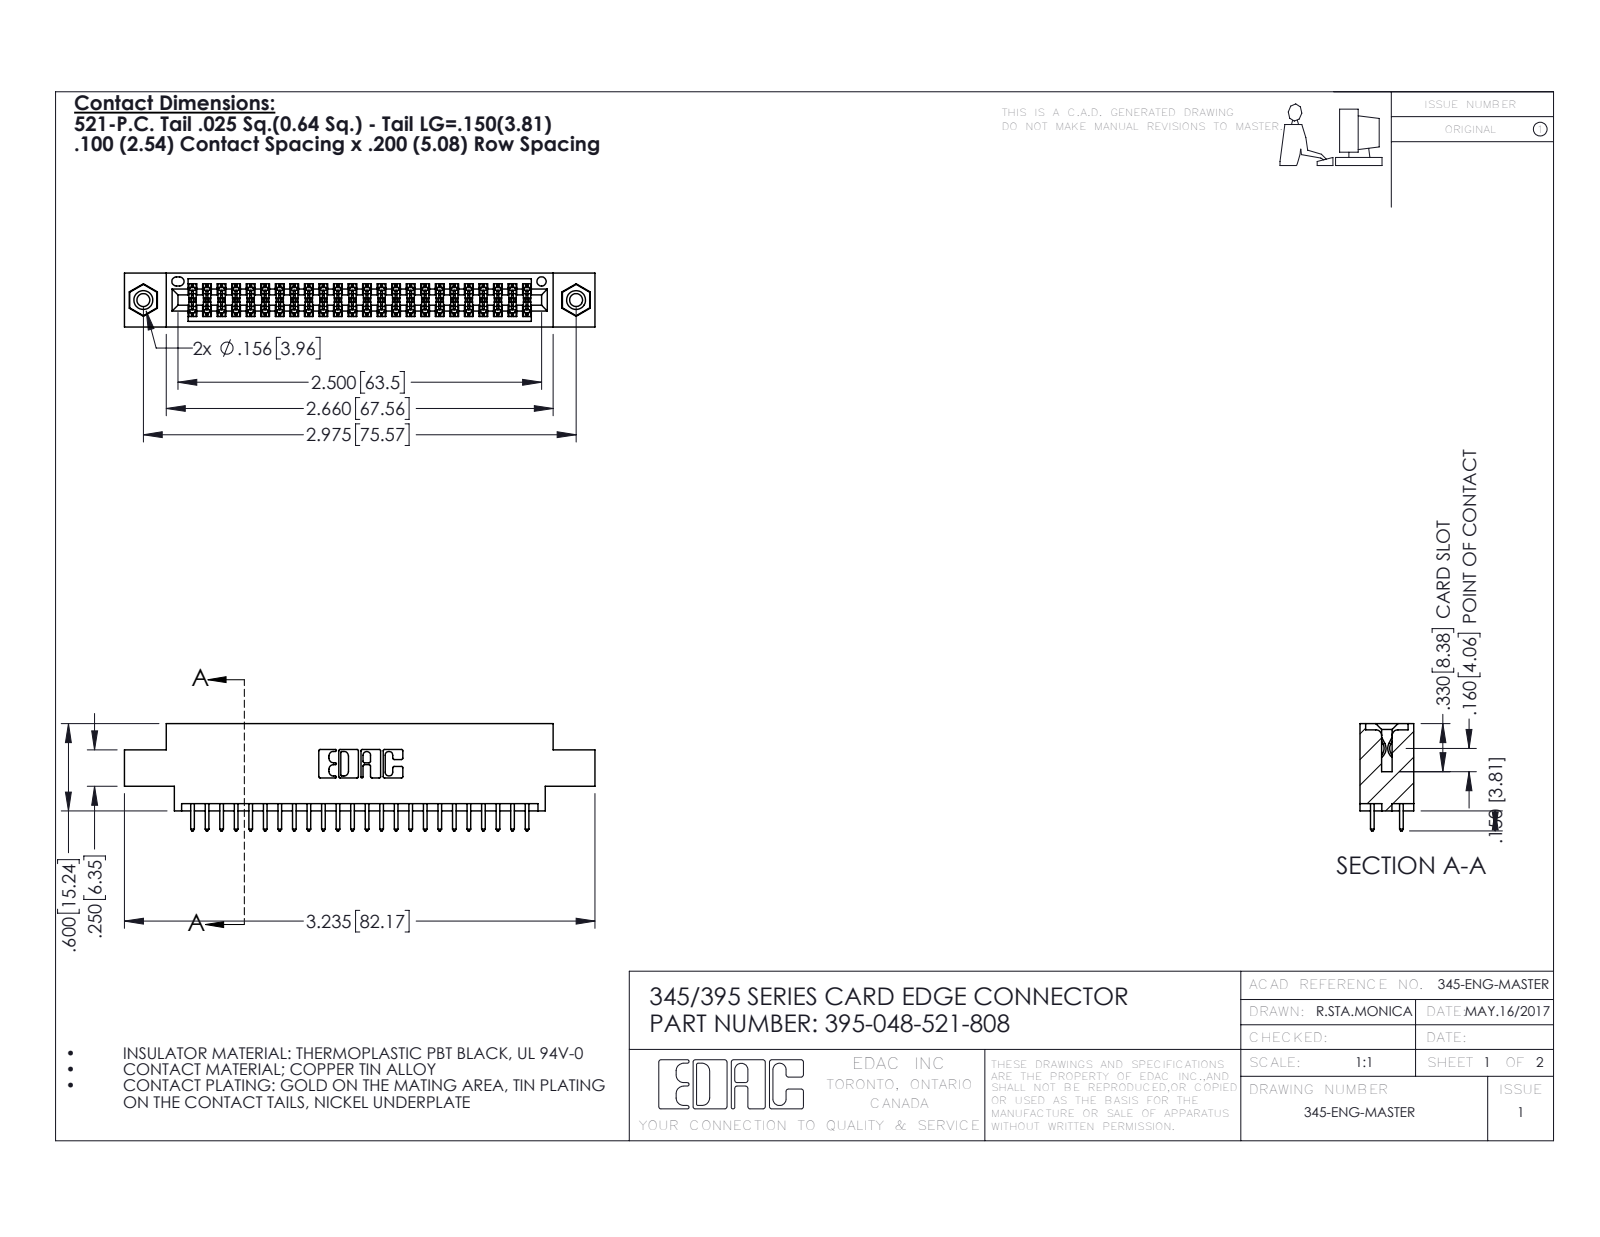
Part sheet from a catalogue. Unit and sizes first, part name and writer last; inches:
Units: inches
Overall size (bounding box): 3.235 × 0.737 × 0.37
Round holes (diameter × count): ⌀0.089 ×2, ⌀0.125 ×2, ⌀0.156 ×2, ⌀0.064 ×1
Round bosses / shafts (diameter × count): ⌀0.155 ×2
Partial cylindrical surfaces — rounded edges, fillets, slot ends (radius × count): R0.006 ×72, R0.01 ×48, R0.01 ×22, R0.007 ×6, R0.031 ×6, R0.026 ×3, R0.014 ×2, R0.019 ×2
Main face-to-face distances: 0.072, 0.298, 0.2, 0.37, 0.098, 0.272, 0.025, 0.225, 0.175, 0.149
Hole centre spacings: 0.27, 2.741, 2.975
Volume: 0.468 in³ · Surface area: 17.09 in²
Bodies: 51 solids, 2590 faces (1700 planar, 874 cylindrical, 16 other)
Part name (STEP PRODUCT): 395-048-521-808; 345-292-001_345-293-121; 345-250-001_345-250-003-102; 345 Part_0.170 Offset - 0.156 Dia-TI
STEP written by: SolidWorks 2016 (CONFIG_CONTROL_DESIGN)
